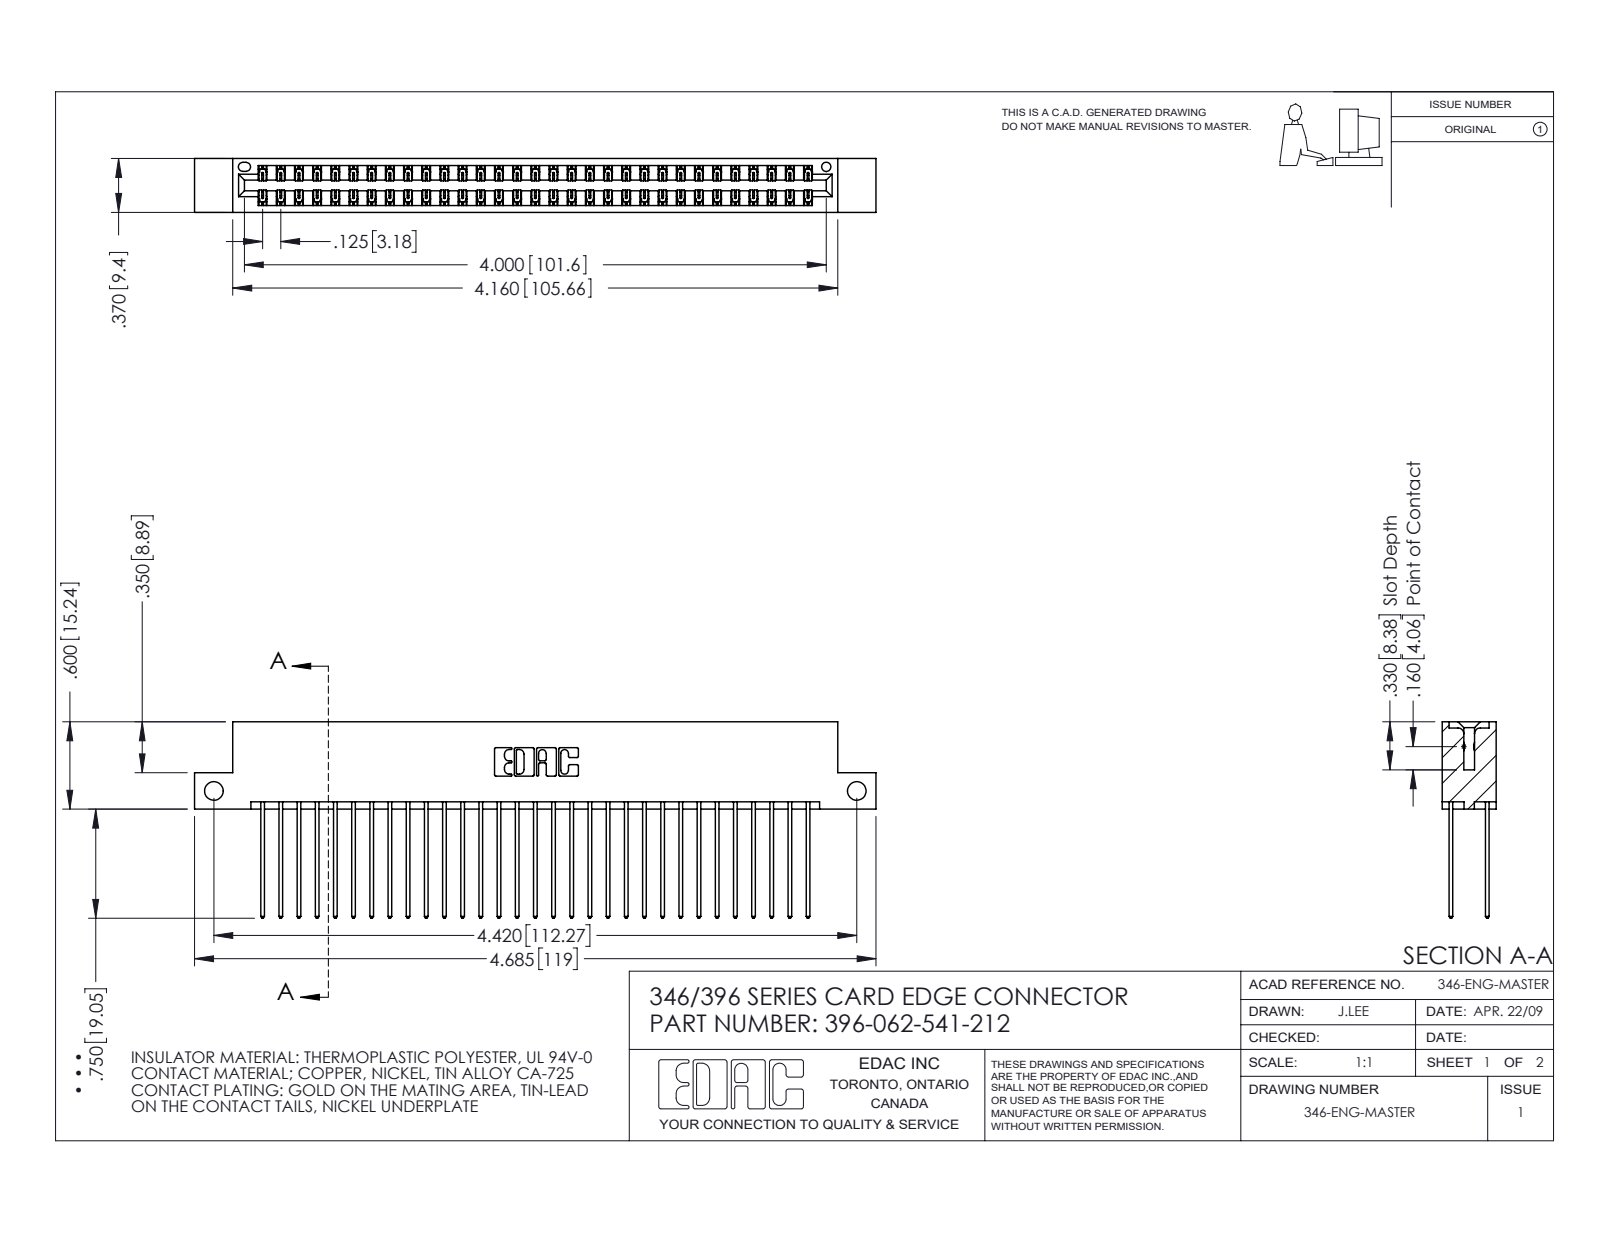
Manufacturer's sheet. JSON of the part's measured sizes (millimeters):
{"part_name": "346 Part_Flush Mounting Lugs - Side Mount; 396-062-541-212; 345-292-001_345-293-141", "step_written_by": "SolidWorks 2016 (CONFIG_CONTROL_DESIGN)", "units": "millimeters", "bodies": {"solids": 63, "faces": 3346, "planar": 2246, "cylindrical": 1100, "other": 0}, "overall_size": [119, 34.3, 9.4], "volume_mm3": 11800, "surface_area_mm2": 17600, "round_holes": [[3.3, 2], [1.6, 1]], "partial_cylinders_radius": [[0.2, 93], [0.3, 62], [0.3, 22], [0.2, 6], [0.8, 6], [0.7, 3], [0.4, 2], [0.6, 2]], "face_to_face_distances": [1.2, 8.2, 6.4, 1.8, 7.6, 0.6, 9.4, 7, 5.7, 3.8], "hole_center_spacings": [112.3]}
